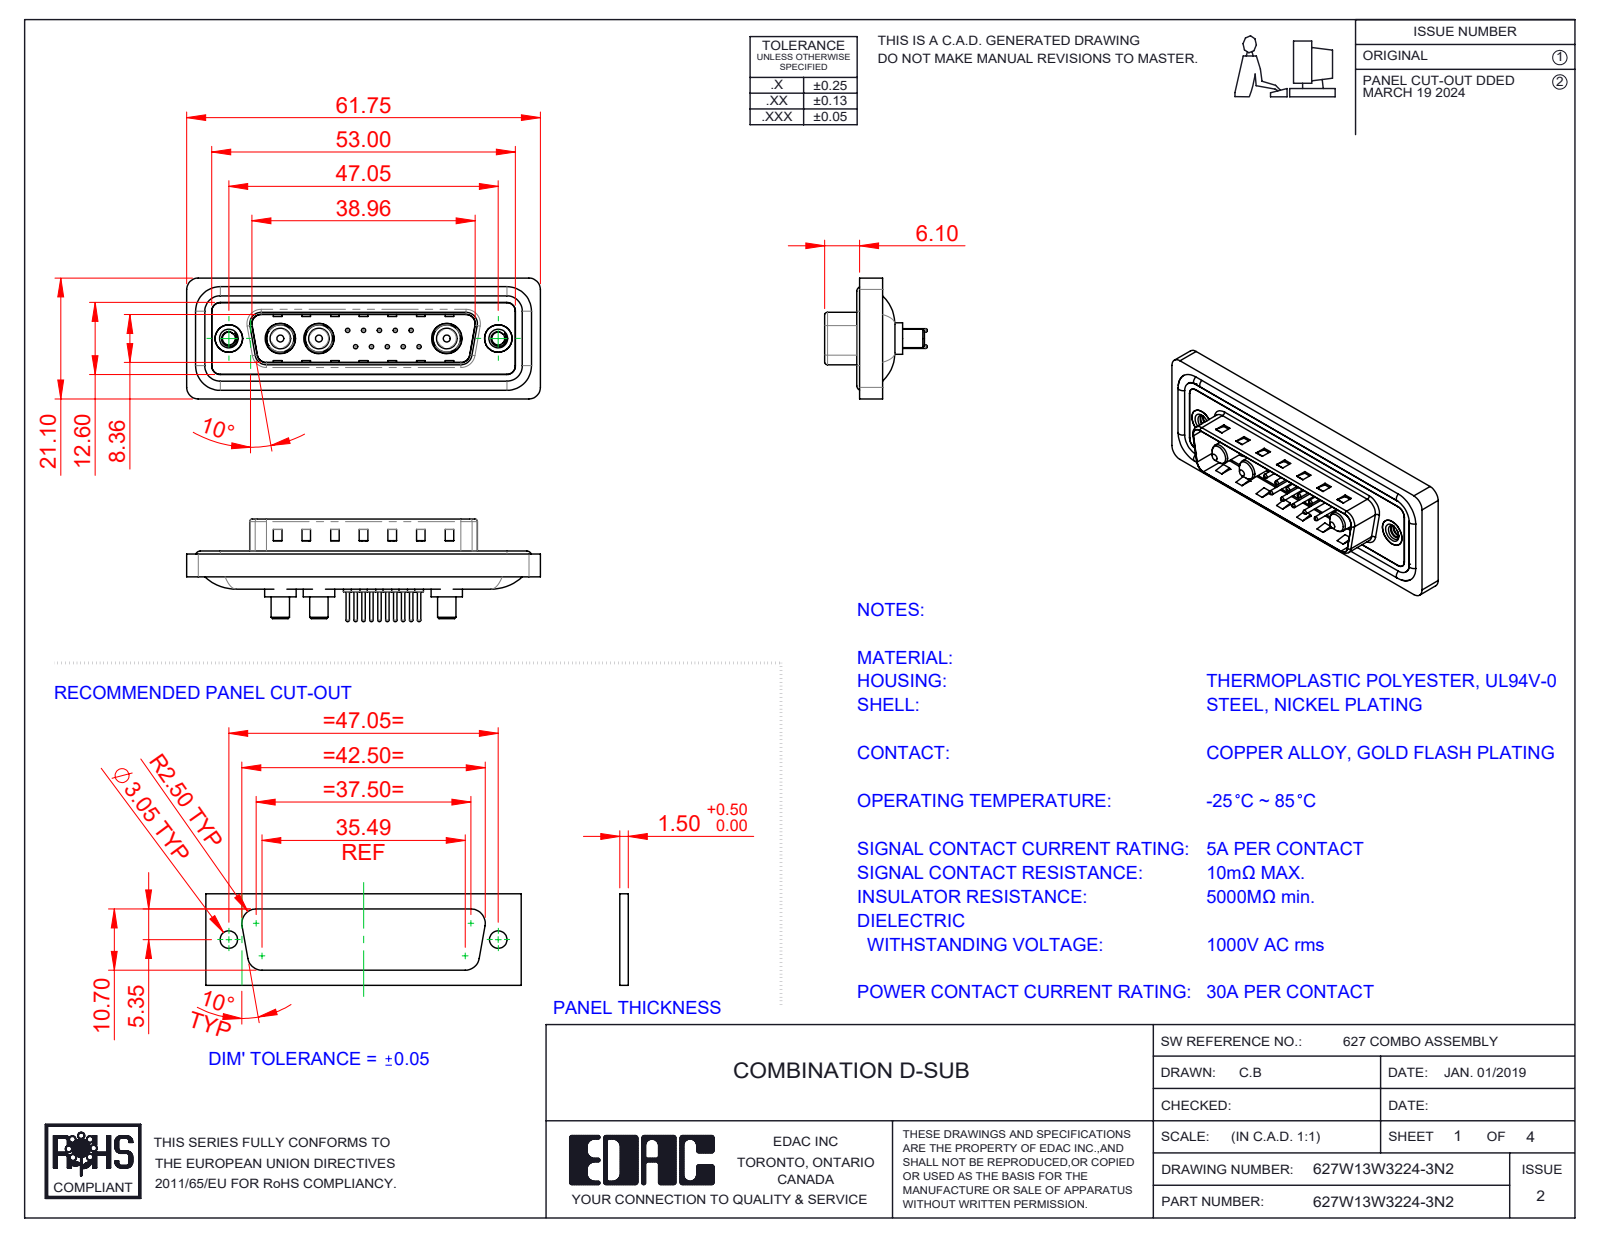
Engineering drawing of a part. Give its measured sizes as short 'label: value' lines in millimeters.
name: 627Combo Shell Rear_25 Contacts; Power Pin_30A S; 627Combo Contact Row 2_24; 627Combo Waterproof Housing_25 Contacts (+5 more)
written by: SolidWorks 2023 (CONFIG_CONTROL_DESIGN)
unit: mm
bodies: 23 solids, 970 faces (309 planar, 385 cylindrical, 276 other)
size: 61.75 × 21.1 × 17.9
volume: 7 357 mm³; area: 11 888 mm²
holes: 10× ⌀0.75, 10× ⌀1.6, 10× ⌀2, 3× ⌀4.85, 3× ⌀5.3, 2× ⌀2.26, 2× ⌀4, 2× ⌀4.8, 2× ⌀5
bosses: 10× ⌀1.5, 10× ⌀0.6, 4× ⌀1.6, 3× ⌀5.5, 3× ⌀5.2, 3× ⌀4.75, 3× ⌀3.75, 3× ⌀3.6
rounds: 22× R1.5, 18× R2, 8× R0.5, 8× R1.6, 4× R0.25, 4× R0.6, 4× R0.65, 4× R0.9
face distances: 0.4, 1.5, 1.1, 1.6, 0.5, 3.1, 2.9, 0.82, 9.58, 4.1
hole spacings: 3.16, 2.77, 5.04, 5.54, 7.49, 5.03, 8.31, 10.11
